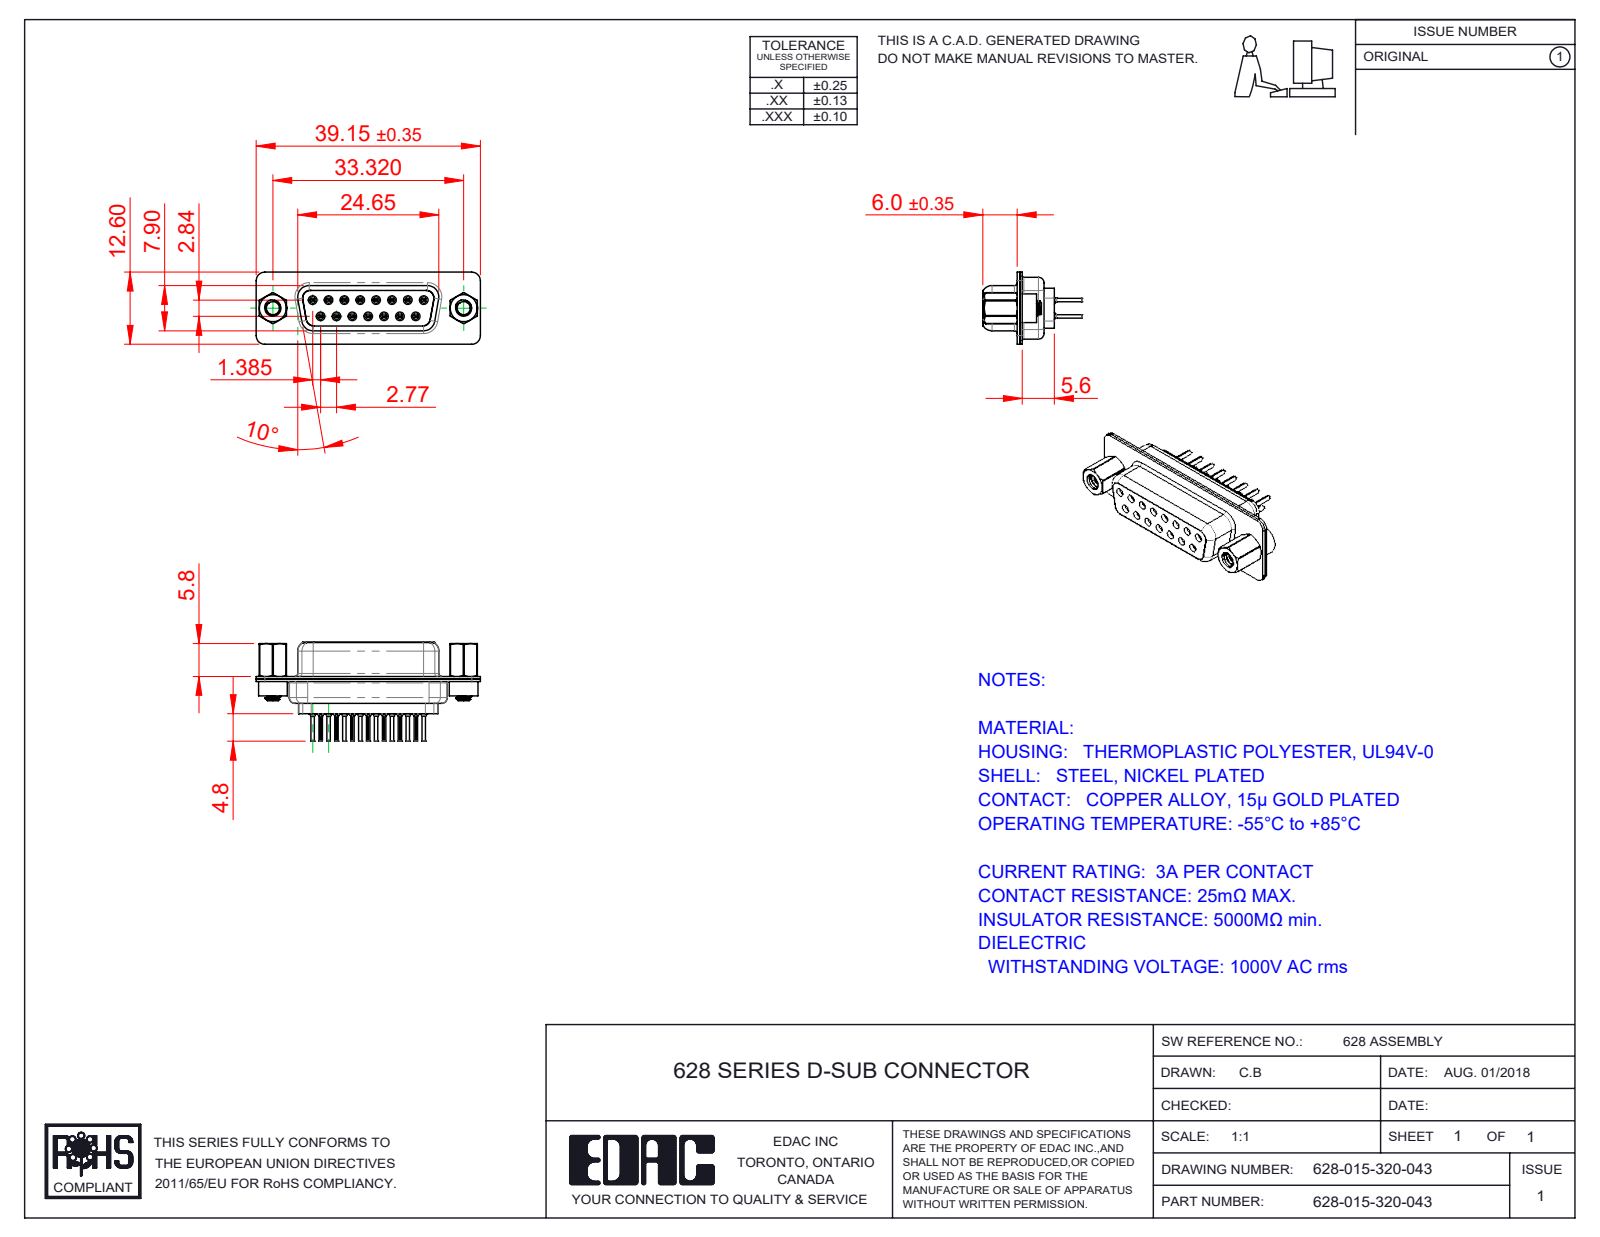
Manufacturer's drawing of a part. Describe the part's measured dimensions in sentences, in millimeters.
The part is named "628 Contact Row 1_20L; 628 Shell Front_15 Contacts; 628-015-320-043; 628 Housing_15 LP (+4 more)". Its 3-D file was written by "SolidWorks 2020 (CONFIG_CONTROL_DESIGN)". It is 22 solids with 2306 faces: 554 planar, 702 cylindrical and 1050 other. Overall it measures 39.15 by 17.3 by 12.6 millimeters. Its volume is 2 750 cubic millimeters and its surface area 6 798 square millimeters. Round holes: 15 of diameter 0.2, 15 of diameter 0.8, 15 of diameter 0.9, 15 of diameter 1.1, 15 of diameter 1.6, 8 of diameter 1.7, 2 of diameter 2.26, 2 of diameter 2.29, 2 of diameter 4, 2 of diameter 4.05, 2 of diameter 4.85. Round bosses or shafts: 15 of diameter 2, 15 of diameter 1.5, 15 of diameter 1.2, 15 of diameter 0.6, 2 of diameter 5, 2 of diameter 4.95, 2 of diameter 4.8, 2 of diameter 2.79. Partial cylindrical surfaces (rounded edges, fillets, slot ends): 30 of radius 0.1, 18 of radius 1.5, 15 of radius 0.28, 12 of radius 2, 8 of radius 1.35, 4 of radius 0.25, 4 of radius 0.5, 4 of radius 0.6. The main face-to-face distances are 0.45, 0.4, 0.9, 6.6, 1.9, 8.5, 1.4, 0.85, 7.05, 7.45. The hole center spacings are 3.16, 2.77, 5.54, 8.31, 11.08, 5.03, 5.04, 7.48.
